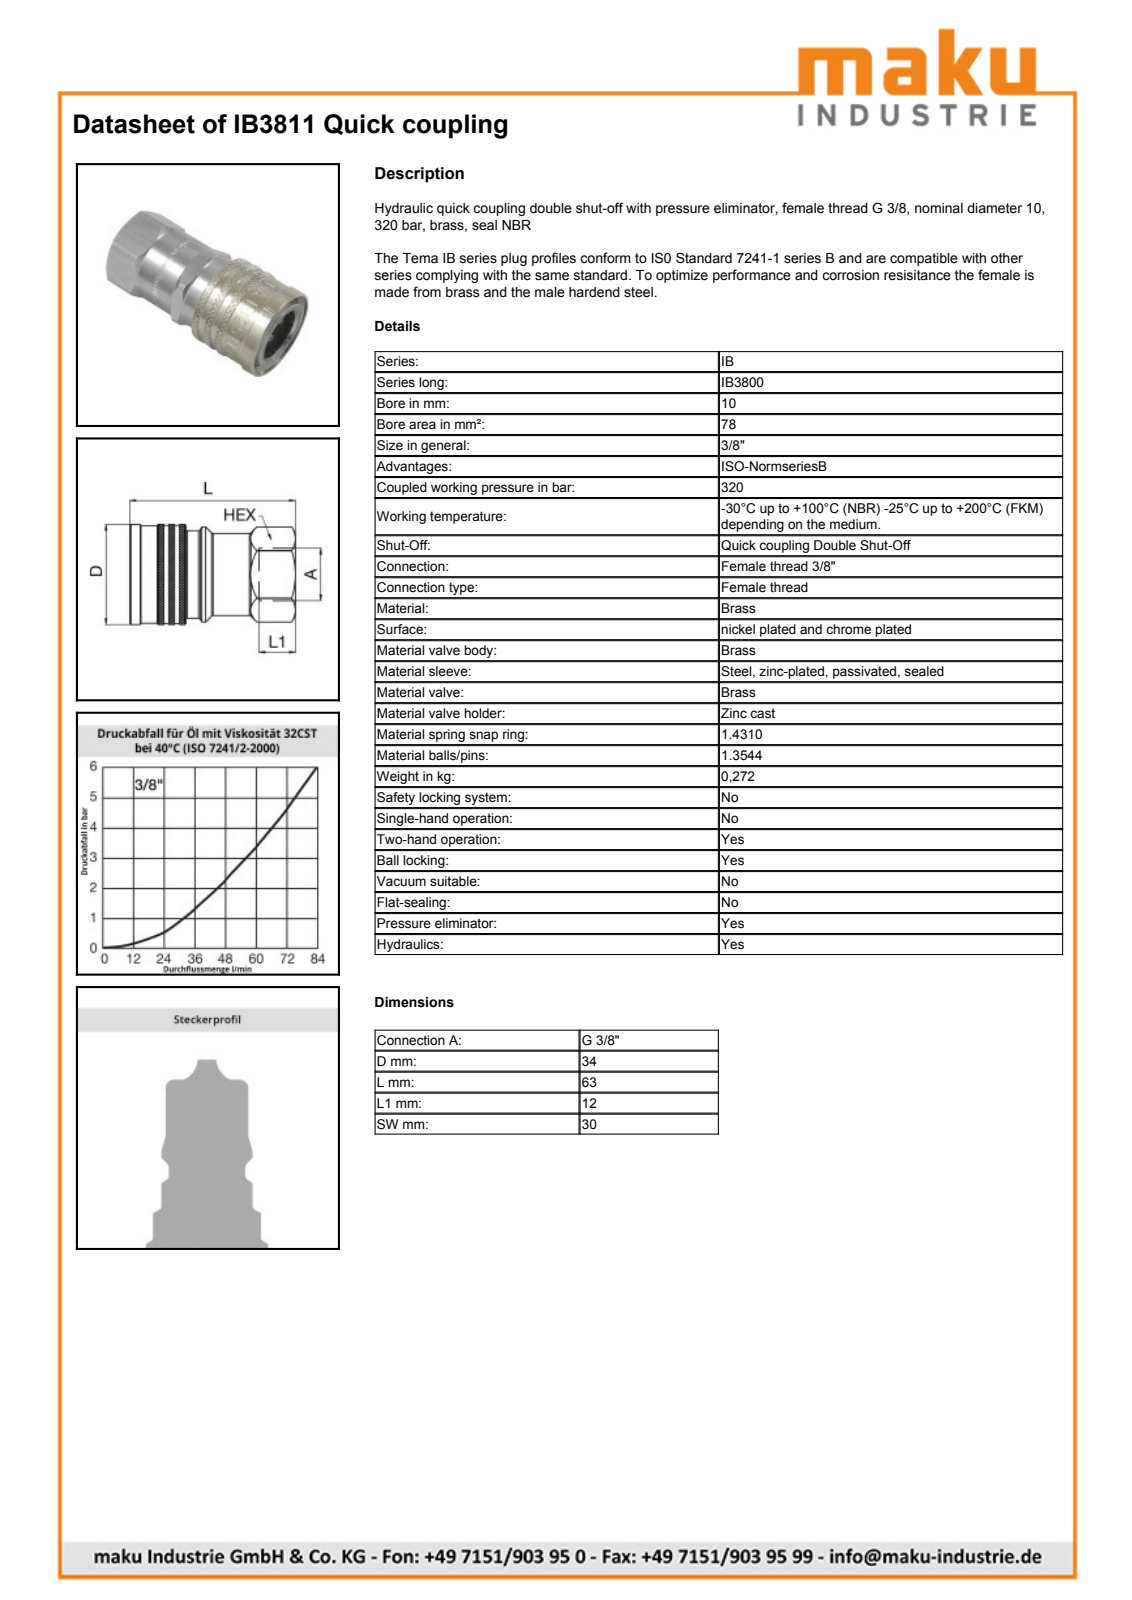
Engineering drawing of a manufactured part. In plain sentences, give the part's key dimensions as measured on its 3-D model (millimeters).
The part is named "IB3811". Its 3-D file was written by "SolidWorks 2009 (AUTOMOTIVE_DESIGN)". It is 1 solid with 257 faces: 33 planar, 74 cylindrical and 150 other. Overall it measures 62.5 by 34 by 34 millimeters. Its volume is 39 363 cubic millimeters and its surface area 11 682 square millimeters. Round holes: 1 of diameter 2.85, 1 of diameter 3.93, 1 of diameter 14.95, 1 of diameter 19.1, 1 of diameter 19.5, 1 of diameter 20.1, 1 of diameter 22.34, 1 of diameter 23.33, 1 of diameter 30.8, 1 of diameter 31.2. Round bosses or shafts: 1 of diameter 34, 1 of diameter 33.2, 1 of diameter 33, 1 of diameter 29.6, 1 of diameter 27.6, 1 of diameter 2.75. Partial cylindrical surfaces (rounded edges, fillets, slot ends): 1 of radius 15.3. The main face-to-face distances are 30, 62.5, 61.45, 1.05, 2, 40, 21.45, 22.5, 2.6, 6.9.
